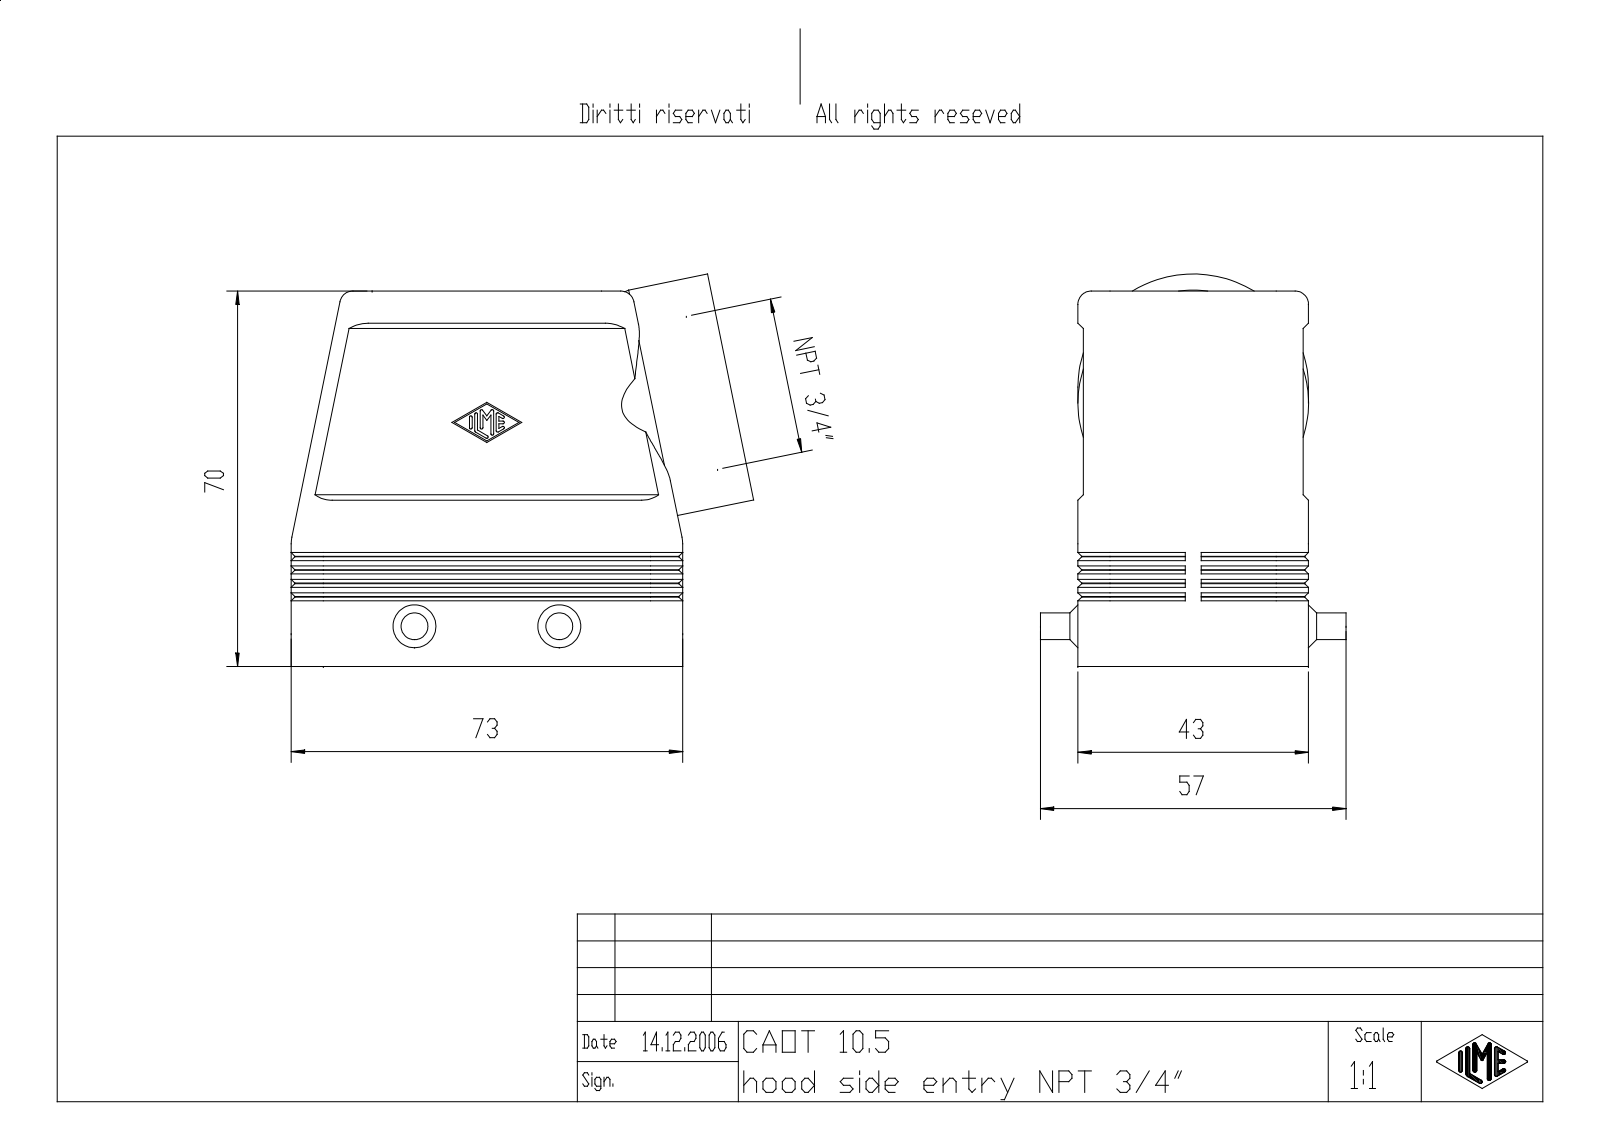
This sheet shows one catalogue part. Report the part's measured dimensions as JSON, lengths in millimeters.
{"part_name": "MSBO6979", "step_written_by": "Creo Elements/Direct Modeling 18.0B 02-Dec-2011 (C) Parametric Technology GmbH (AUTOMOTIVE_DESIGN)", "units": "millimeters", "bodies": {"solids": 1, "faces": 340, "planar": 181, "cylindrical": 101, "other": 58}, "overall_size": [86.24, 73.17, 57], "volume_mm3": 68346, "surface_area_mm2": 36692, "round_holes": [[4, 4], [2.46, 3], [2.46, 1]], "round_bosses_or_shafts": [[5, 2], [43, 1]], "partial_cylinders_radius": [[0.25, 14], [6, 12], [2, 4], [2.5, 4], [3, 4], [5.3, 4]], "face_to_face_distances": [2, 3, 39, 37, 1, 40, 42, 9, 12, 41], "hole_center_spacings": [27, 57, 63.07]}
